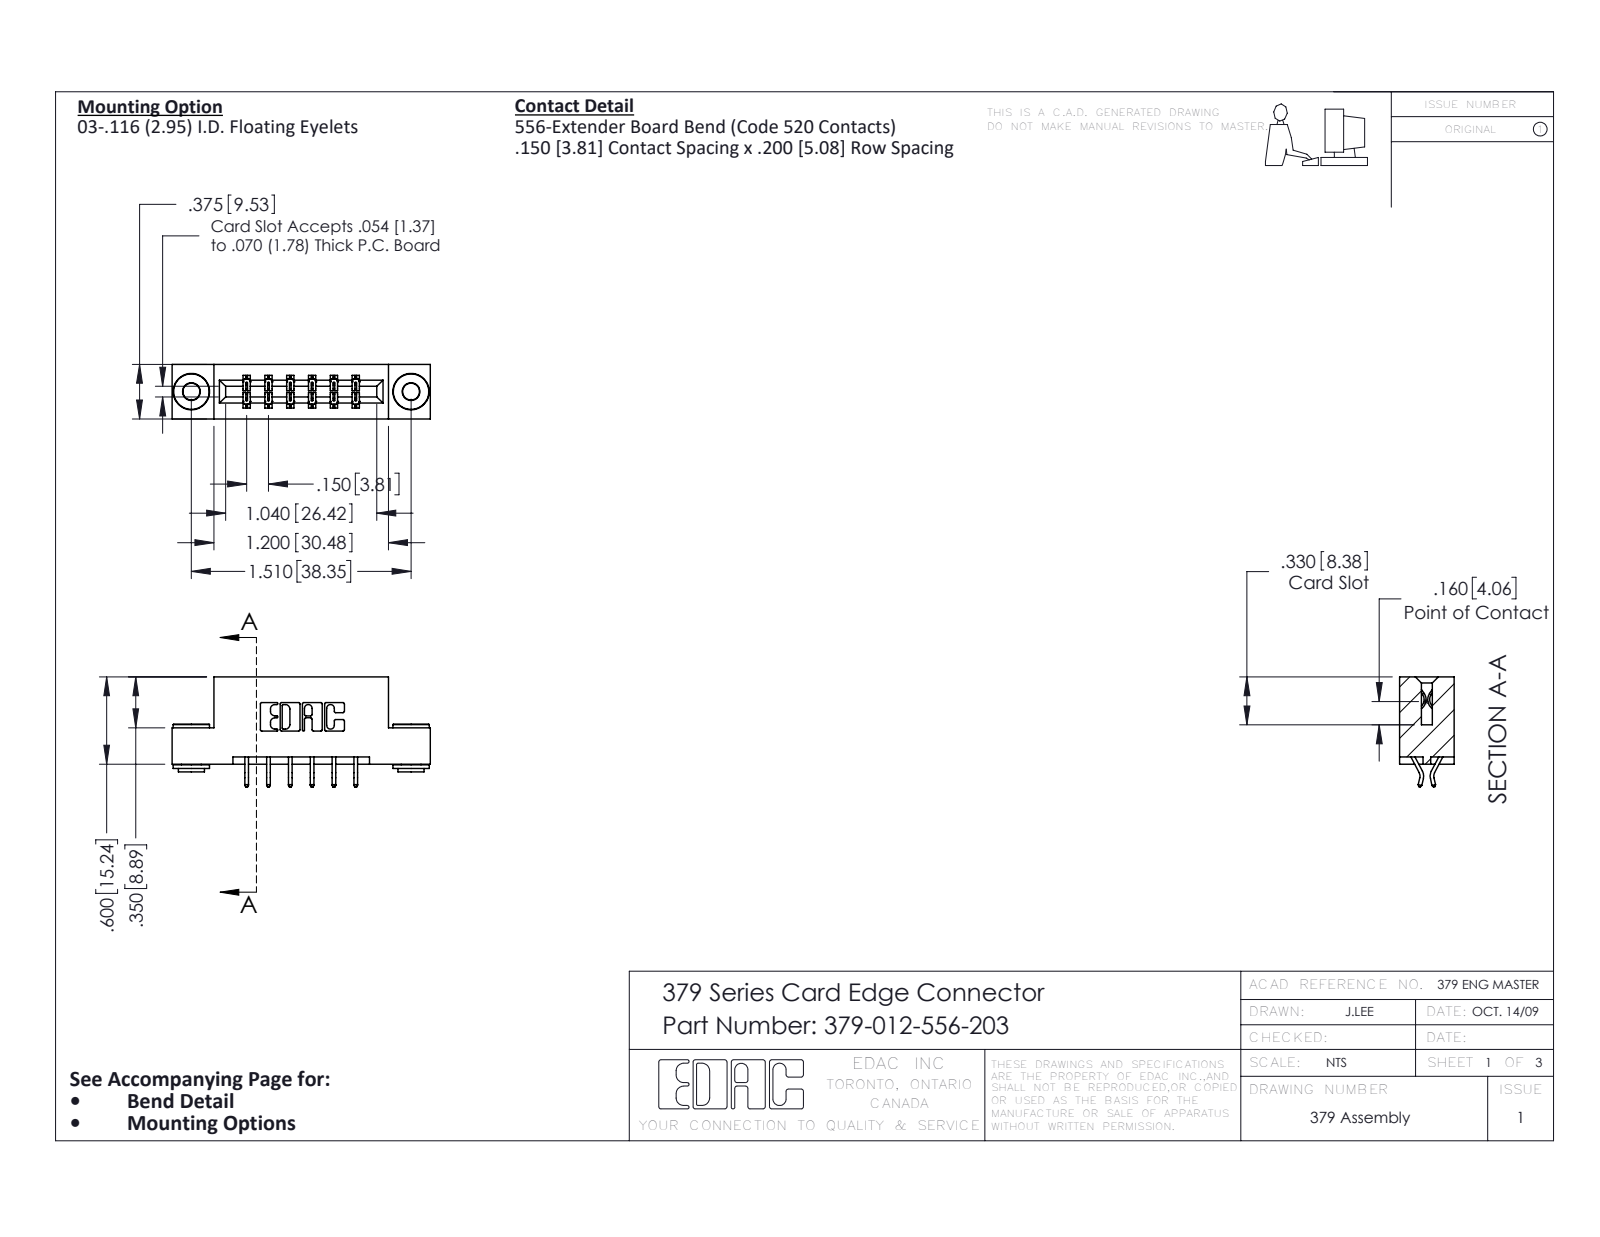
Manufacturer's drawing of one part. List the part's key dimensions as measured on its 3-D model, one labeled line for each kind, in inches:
Part name (STEP PRODUCT): 345-292-001_556 Tail; 379 Part_Flush - .156 Dia - TH; 379-012-556-203; 345-250-002_345-250-002-102
STEP written by: SolidWorks 2016 (CONFIG_CONTROL_DESIGN)
Units: inches
Bodies: 15 solids, 848 faces (560 planar, 280 cylindrical, 8 other)
Overall size (bounding box): 1.775 × 0.757 × 0.375
Volume: 0.266 in³ · Surface area: 7.417 in²
Round holes (diameter × count): ⌀0.116 ×2, ⌀0.156 ×2
Round bosses / shafts (diameter × count): ⌀0.25 ×2, ⌀0.18 ×2, ⌀0.136 ×2
Partial cylindrical surfaces — rounded edges, fillets, slot ends (radius × count): R0.01 ×22, R0.006 ×18, R0.007 ×6, R0.031 ×6, R0.026 ×3, R0.01 ×2, R0.014 ×2, R0.022 ×2
Main face-to-face distances: 0.3, 0.2, 0.05, 0.15, 0.375, 0.25, 0.35, 0.1, 0.075, 0.55
Hole centre spacings: 1.51
